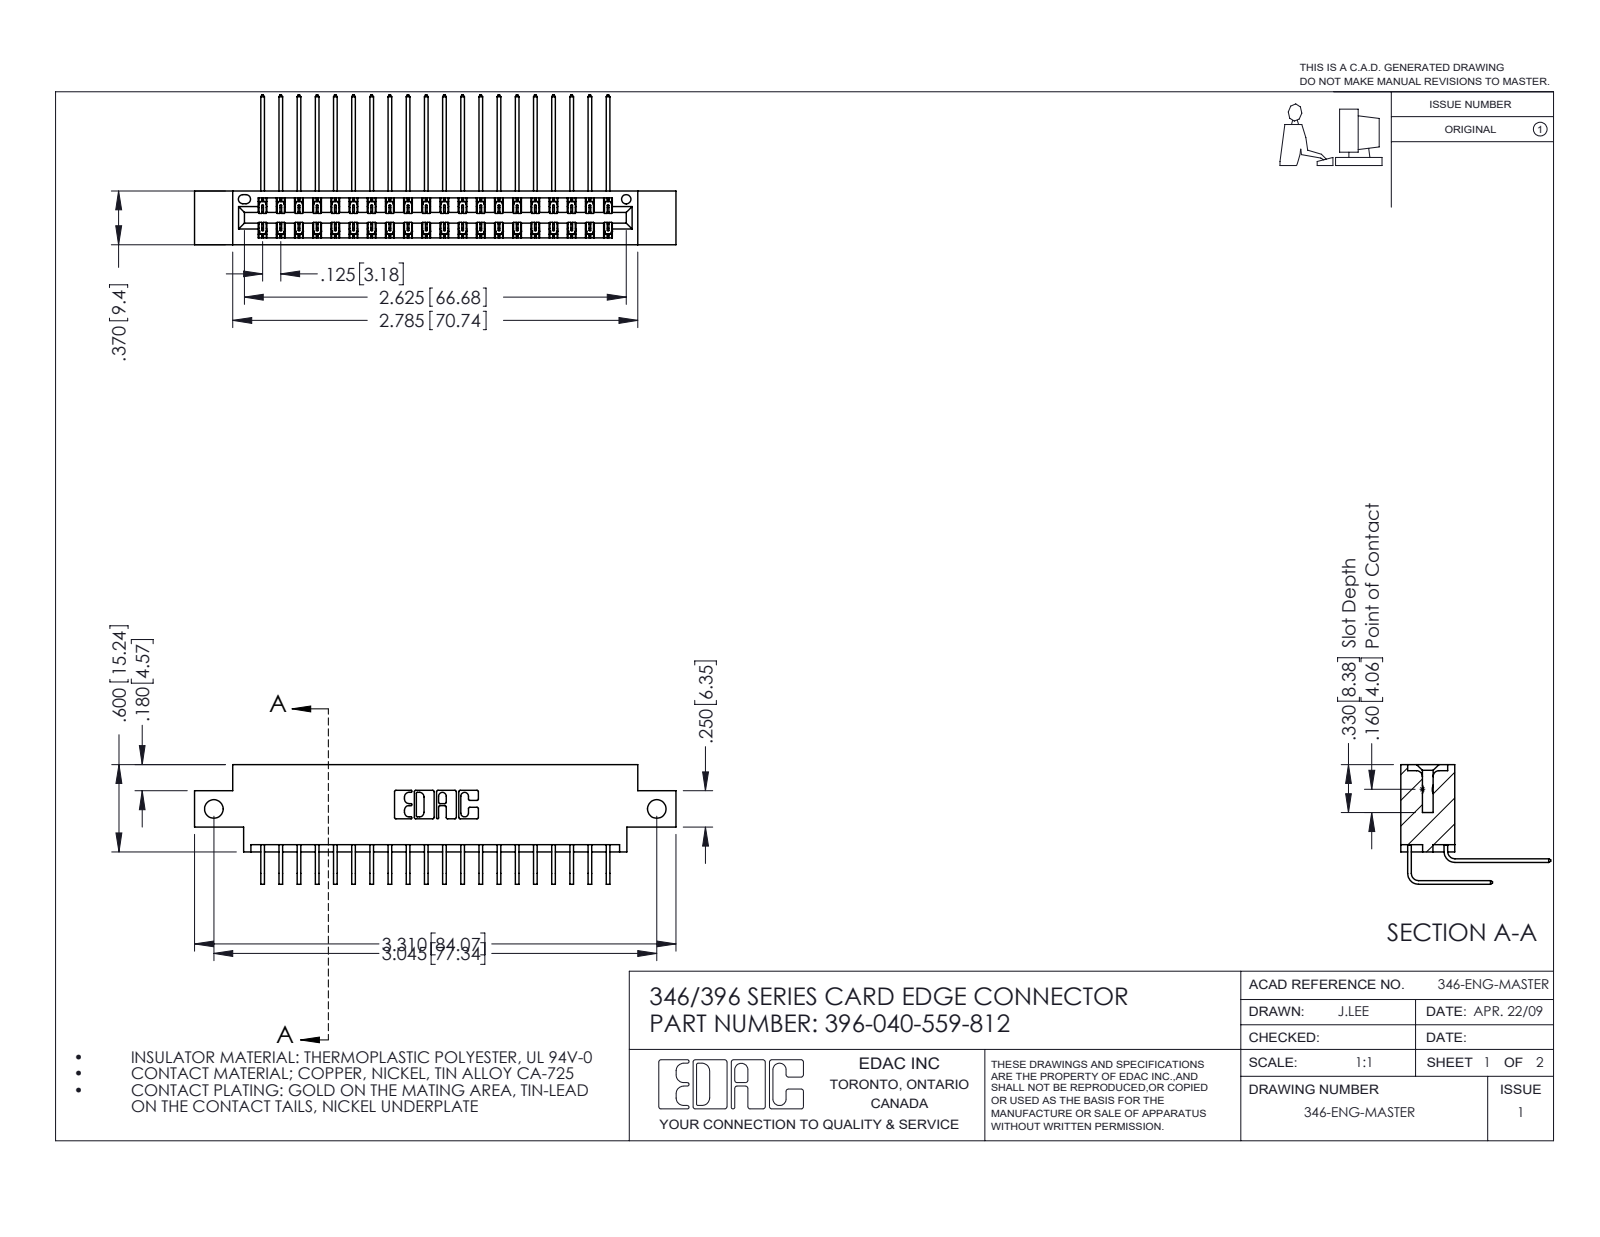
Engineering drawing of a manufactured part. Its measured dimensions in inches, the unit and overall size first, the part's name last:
Units: inches
Overall size (bounding box): 3.31 × 1.03 × 0.823
Round holes (diameter × count): ⌀0.128 ×2, ⌀0.064 ×1
Partial cylindrical surfaces — rounded edges, fillets, slot ends (radius × count): R0.006 ×60, R0.01 ×22, R0.007 ×6, R0.031 ×6, R0.026 ×3, R0.014 ×2, R0.022 ×2, R0.024 ×2
Main face-to-face distances: 0.048, 0.322, 0.37, 0.25, 0.025, 0.072, 0.298, 0.275, 0.15, 0.148
Hole centre spacings: 3.045
Volume: 0.489 in³ · Surface area: 18.32 in²
Bodies: 41 solids, 2286 faces (1560 planar, 726 cylindrical, 0 other)
Part name (STEP PRODUCT): 345-292-001_559 Tail - 2; 396-040-559-812; 345-292-001_558 559 Tail - 1; 346 Part_0.170 Offset - Side Mount
STEP written by: SolidWorks 2016 (CONFIG_CONTROL_DESIGN)
